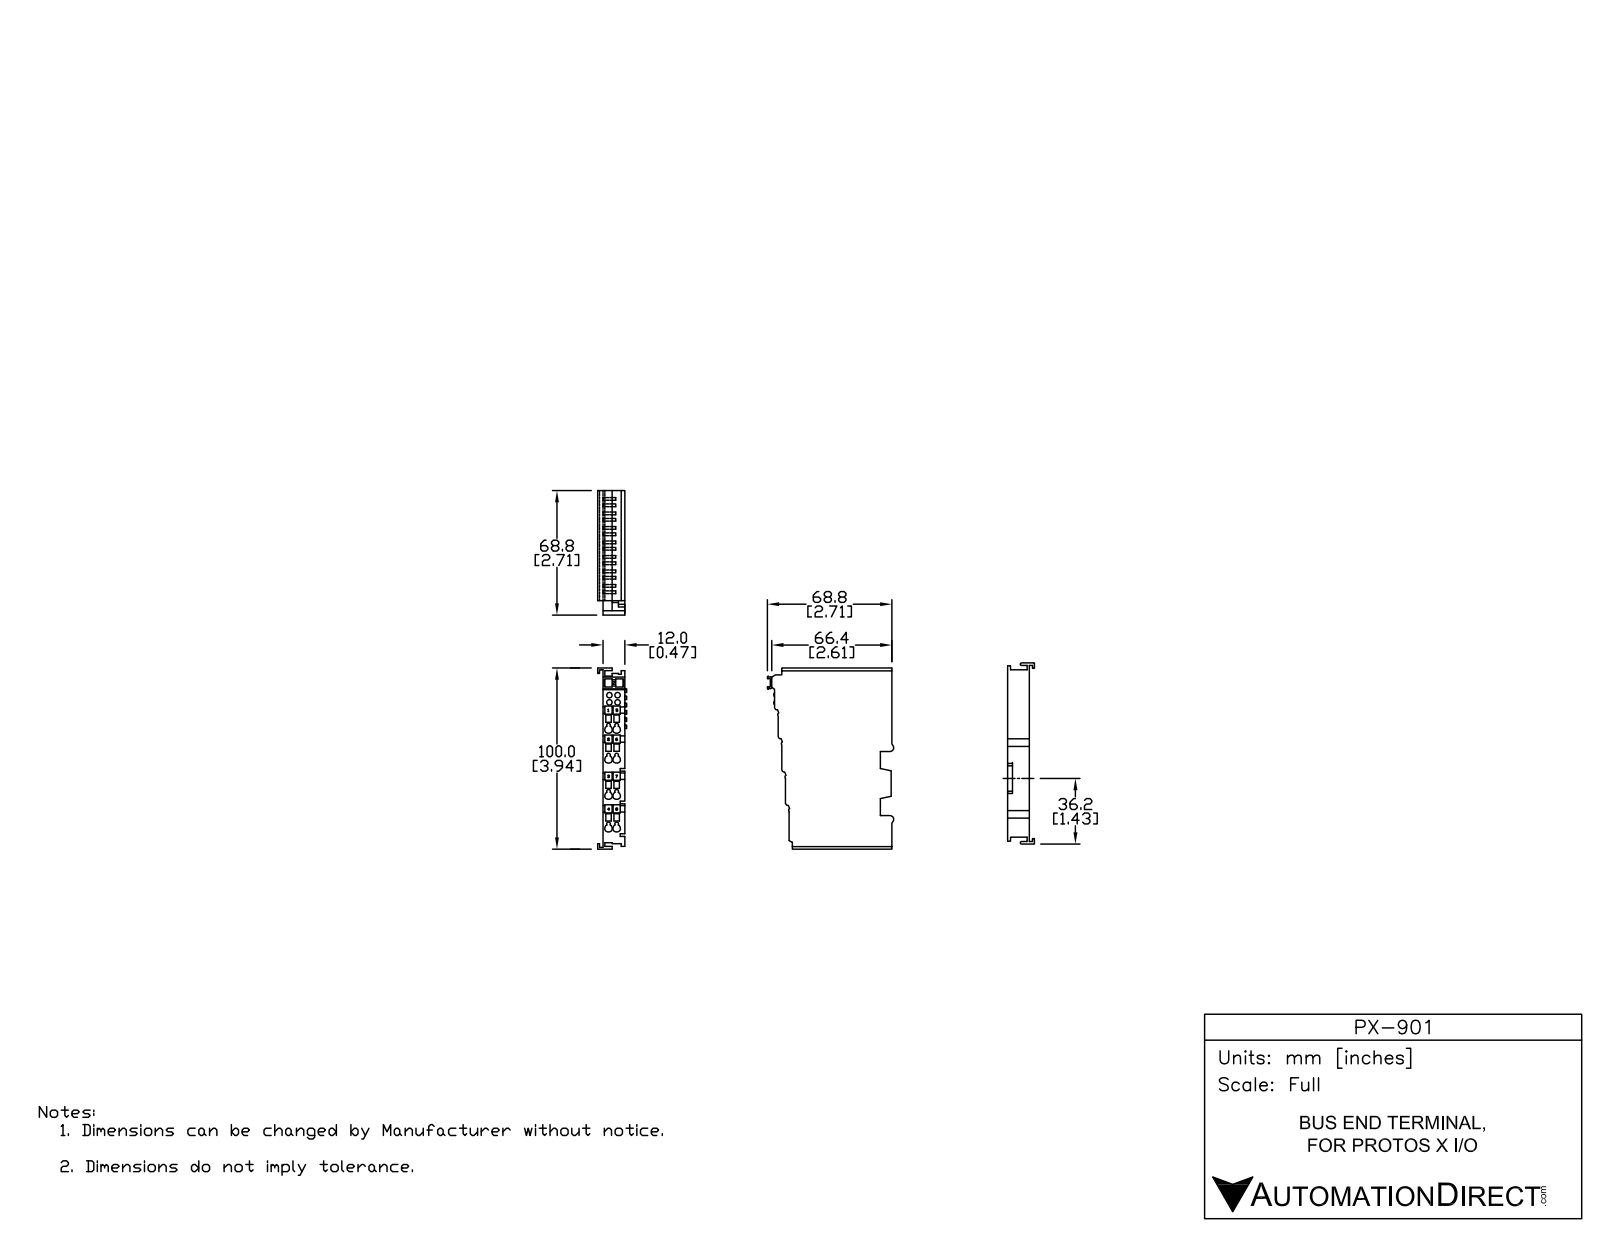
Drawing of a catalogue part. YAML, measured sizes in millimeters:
part_name: "PX-901"
step_written_by: "SolidWorks 2014 (AUTOMOTIVE_DESIGN)"
units: millimeters
bodies: {solids: 20, faces: 1295, planar: 915, cylindrical: 320, other: 60}
overall_size: [100.25, 71.26, 15.15]
volume: 58326
surface_area: 33519
round_holes:
  - {diameter: 4, count: 8}
  - {diameter: 3.5, count: 4}
partial_cylinders:
  - {radius: 0.3, count: 46}
  - {radius: 0.25, count: 35}
  - {radius: 0.38, count: 12}
  - {radius: 0.12, count: 10}
  - {radius: 1, count: 9}
  - {radius: 0.17, count: 4}
  - {radius: 1.03, count: 4}
  - {radius: 1.38, count: 4}
face_to_face_distances: [12, 1, 2, 10, 1.85, 11, 8.7, 4, 3.15, 1.22]
hole_center_spacings: [4.5, 5, 18.4, 19.07, 6.36, 16, 16.76, 20.41]
